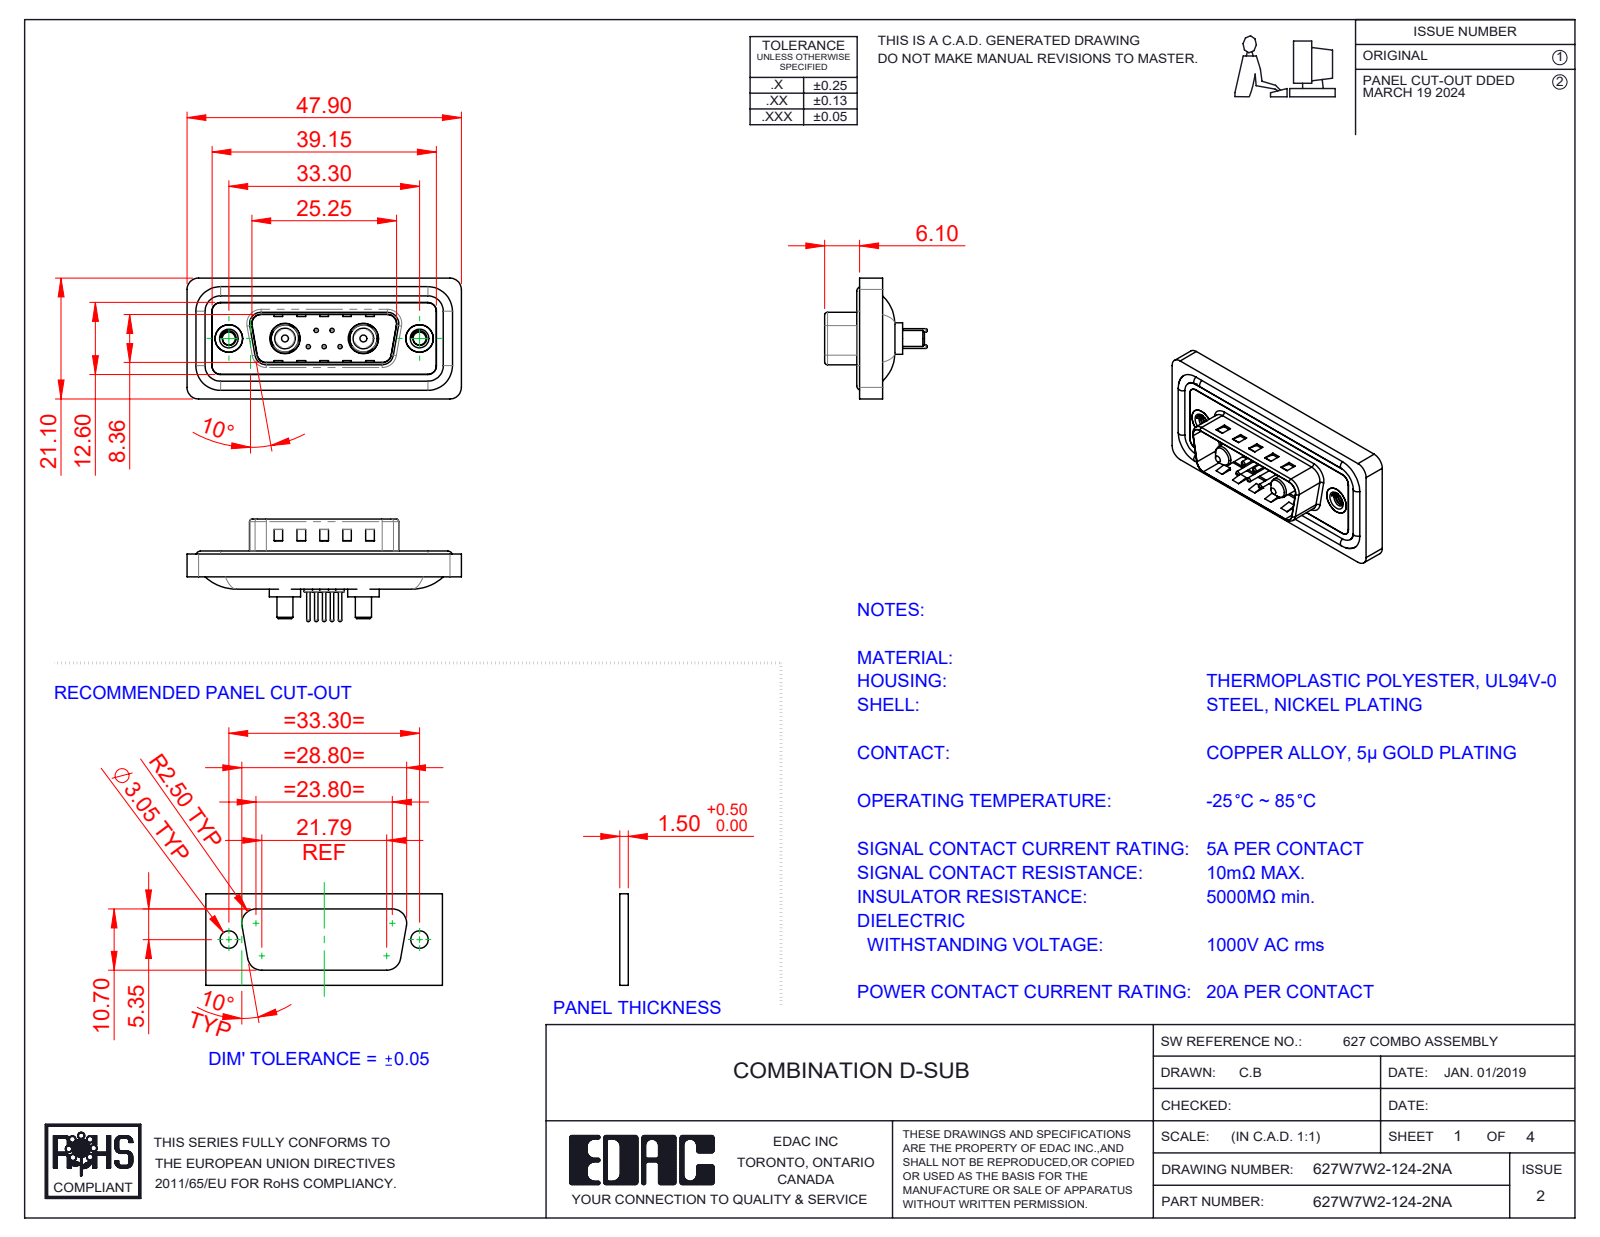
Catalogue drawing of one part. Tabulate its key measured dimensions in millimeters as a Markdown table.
| quantity | value |
| --- | --- |
| part name | 627Combo Contact Row 2_24; 627W7W2-124-2NA; 627Combo Contact Row 1_24; 627Combo Housing_7W2 (+5 more) |
| STEP written by | SolidWorks 2023 (CONFIG_CONTROL_DESIGN) |
| units | millimeters |
| bodies | 16 solids, 708 faces (232 planar, 294 cylindrical, 182 other) |
| overall size | 47.9 × 21.1 × 17.9 |
| volume | 5 518 mm³ |
| surface area | 8 790 mm² |
| round holes (diameter × count) | 0.75 × 5, 1.6 × 5, 2 × 5, 2.26 × 2, 4 × 2, 4.8 × 2, 4.85 × 2, 5 × 2, 5.3 × 2 |
| round bosses / shafts (diameter × count) | 1.5 × 5, 0.6 × 5, 1.6 × 4, 5.5 × 2, 5.2 × 2, 4.9 × 2, 4.75 × 2, 3.75 × 2 |
| partial cylindrical surfaces (radius × count) | 1.5 × 26, 2 × 20, 0.5 × 8, 1.6 × 8, 0.25 × 4, 0.6 × 4, 0.65 × 4, 0.9 × 4 |
| main face-to-face distances | 0.4, 1.1, 1.5, 1.6, 0.5, 3.1, 2.9, 0.82, 9.58, 4 |
| hole center spacings | 3.16, 2.77, 9.8, 23.5, 4.31, 4.33, 5.03, 5.04 |
